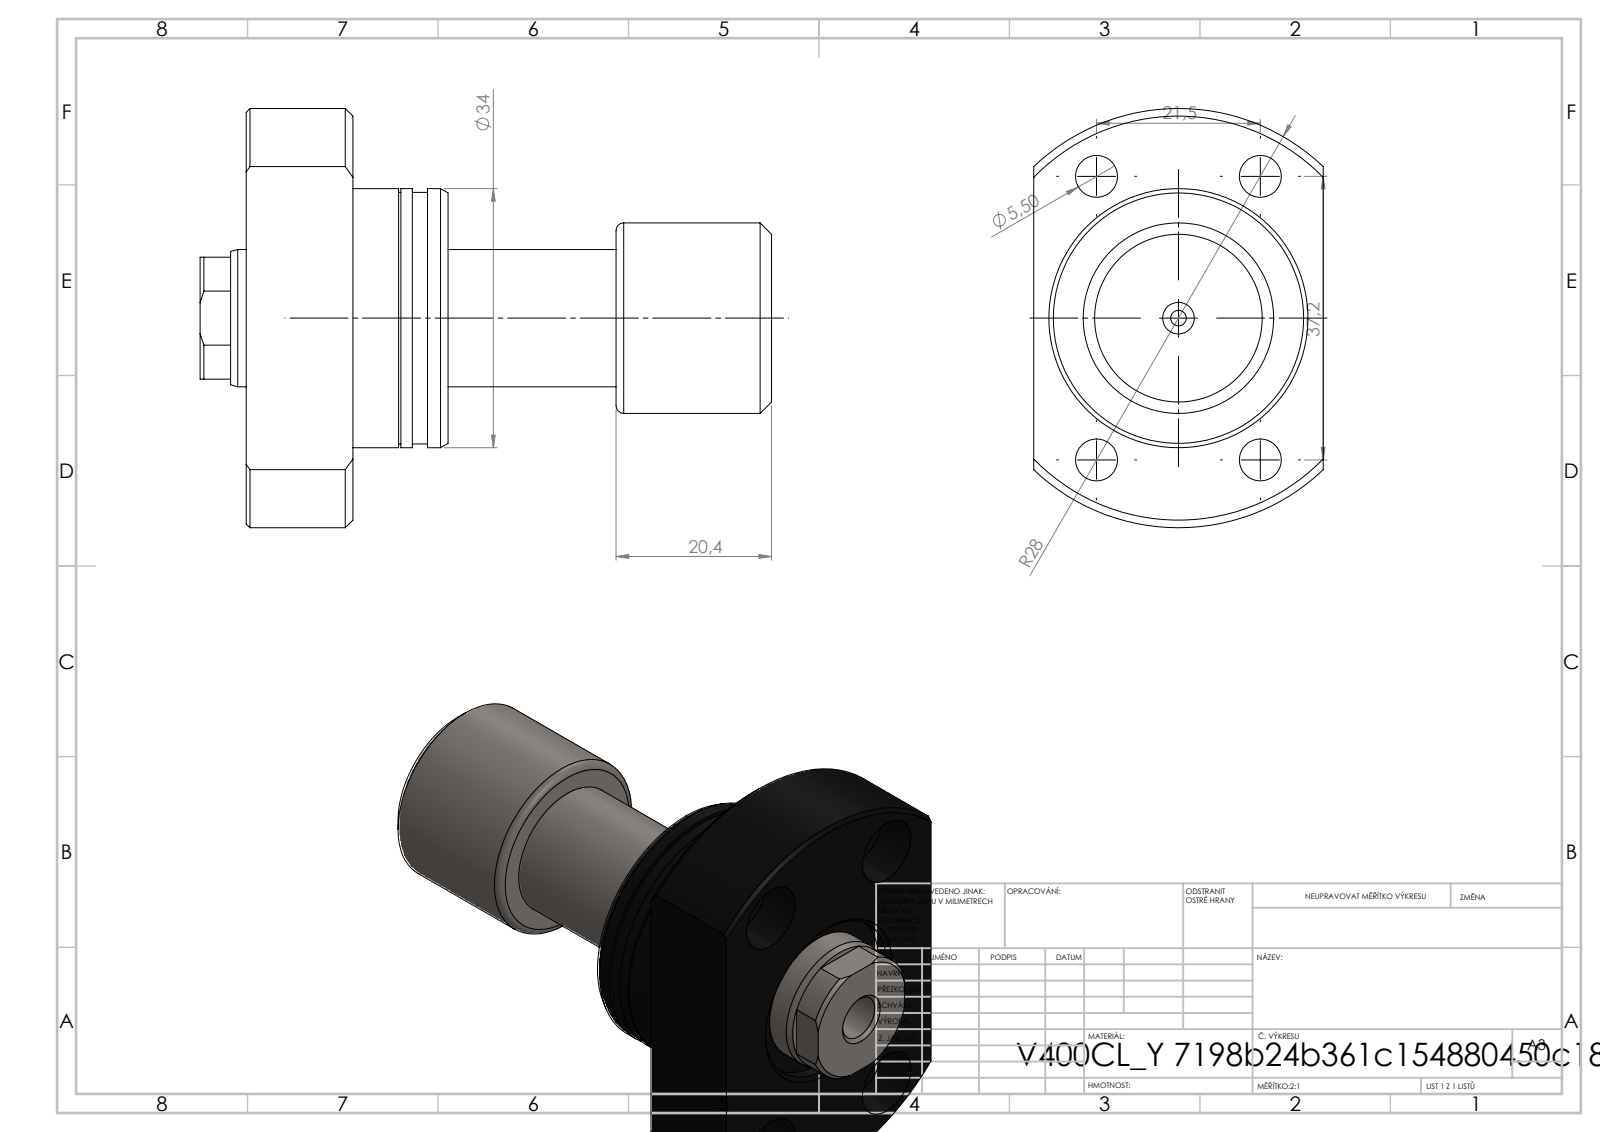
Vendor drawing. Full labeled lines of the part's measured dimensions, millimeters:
Part name (STEP PRODUCT): V400CL_PC_Y; V400CL_VC_X
STEP written by: SolidWorks 2019 (CONFIG_CONTROL_DESIGN)
Units: millimetres
Bodies: 2 solids, 103 faces (26 planar, 47 cylindrical, 30 other)
Overall size (bounding box): 75 × 55 × 38
Volume: 51 705 mm³ · Surface area: 15 444 mm²
Round holes (diameter × count): ⌀5.5 ×4, ⌀9 ×4, ⌀2.05 ×1, ⌀5 ×1, ⌀6 ×1, ⌀18 ×1, ⌀22.5 ×1
Round bosses / shafts (diameter × count): ⌀34 ×1, ⌀33 ×1, ⌀25 ×1
Partial cylindrical surfaces — rounded edges, fillets, slot ends (radius × count): R8.75 ×1, R27.5 ×1
Main face-to-face distances: 14, 38, 12.5, 26.5, 42.45, 54.95, 68.95, 2, 3.5, 22.05
Hole centre spacings: 21.48, 21.5, 37.2, 42.97
